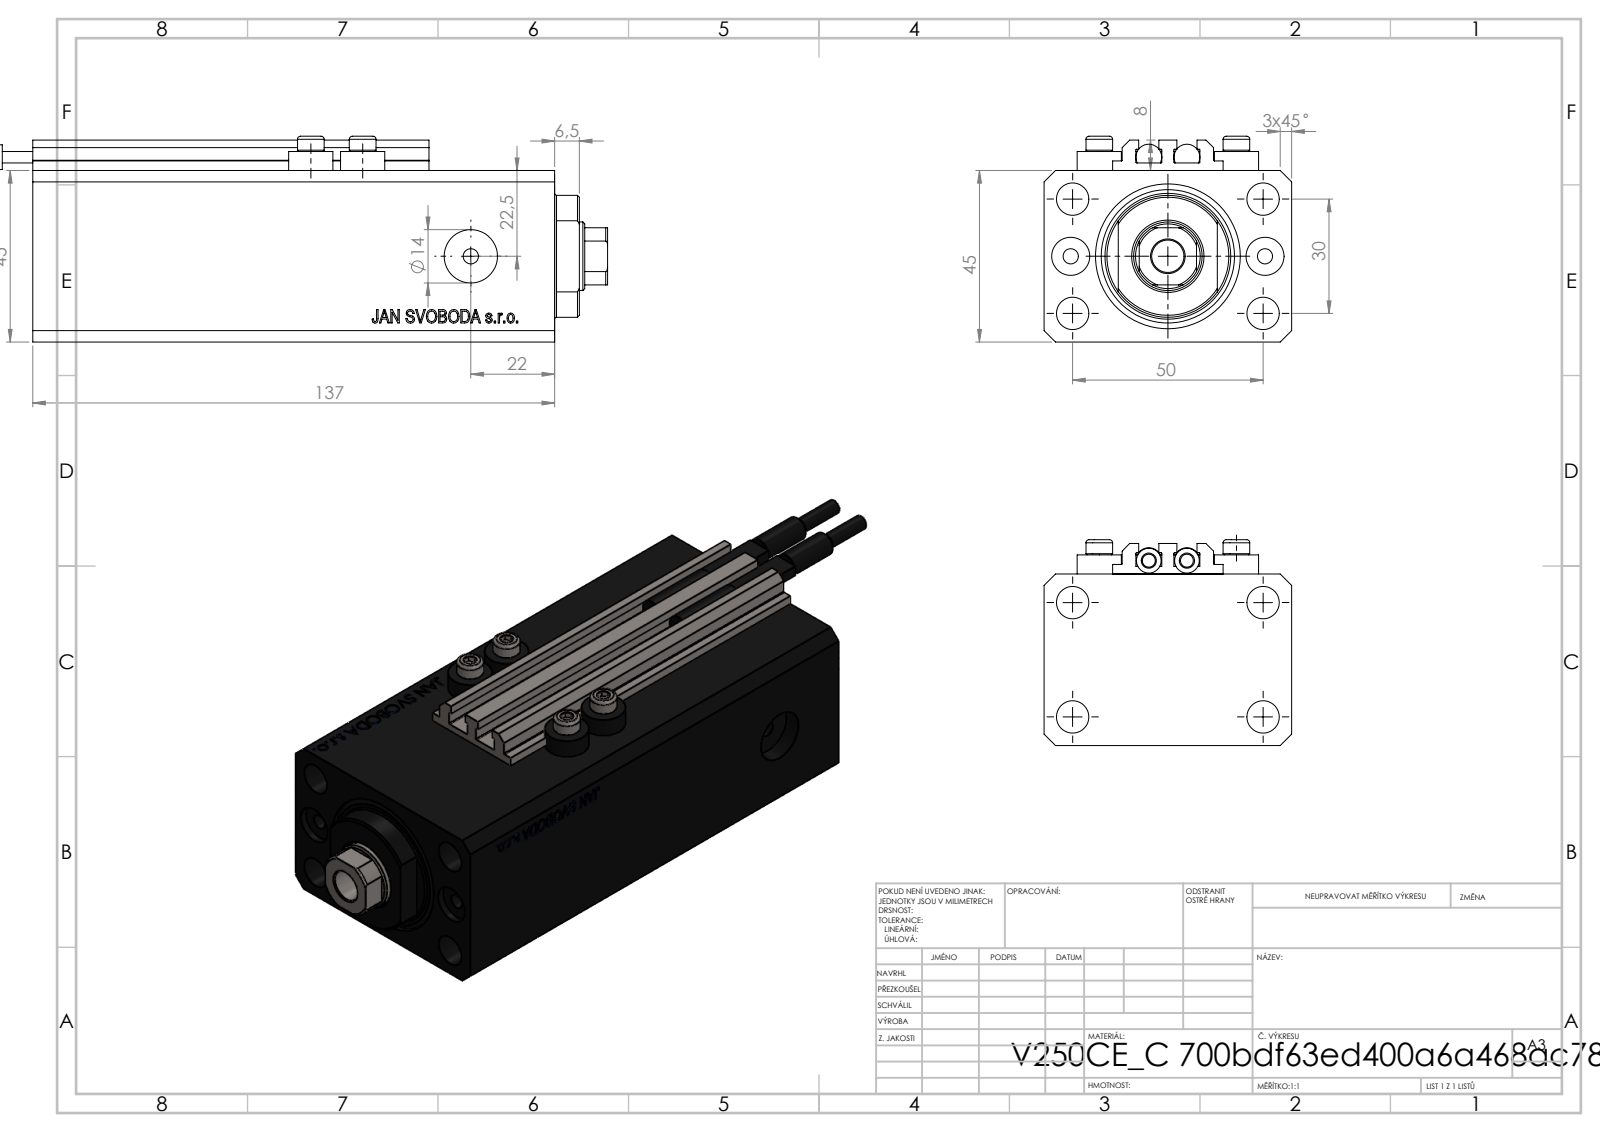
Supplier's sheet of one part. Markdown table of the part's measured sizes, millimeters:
| quantity | value |
| --- | --- |
| part name | SWITCH_V250CE; V250CE_C_Body; V250CE_C_VCP; ALLEN BOLT V250CE (+1 more) |
| STEP written by | SolidWorks 2019 (CONFIG_CONTROL_DESIGN) |
| units | millimeters |
| bodies | 10 solids, 1085 faces (535 planar, 98 cylindrical, 452 other) |
| overall size | 186.9 × 65 × 54 |
| volume | 369 649 mm³ |
| surface area | 95 514 mm² |
| round holes (diameter × count) | 4 × 8, 8.5 × 5, 10 × 2, 14 × 2, 18 × 1, 25 × 1, 38 × 1 |
| round bosses / shafts (diameter × count) | 11.6 × 4, 7 × 4, 6.8 × 2, 6.5 × 2, 4 × 2 |
| partial cylindrical surfaces (radius × count) | 0.2 × 10, 8.5 × 1, 16 × 1 |
| main face-to-face distances | 45, 65, 47, 2, 25.1, 111.9, 2.5, 3, 137, 10 |
| hole center spacings | 15.01, 29.15, 52.68, 13.6, 25.5, 30, 36, 38.48 |
